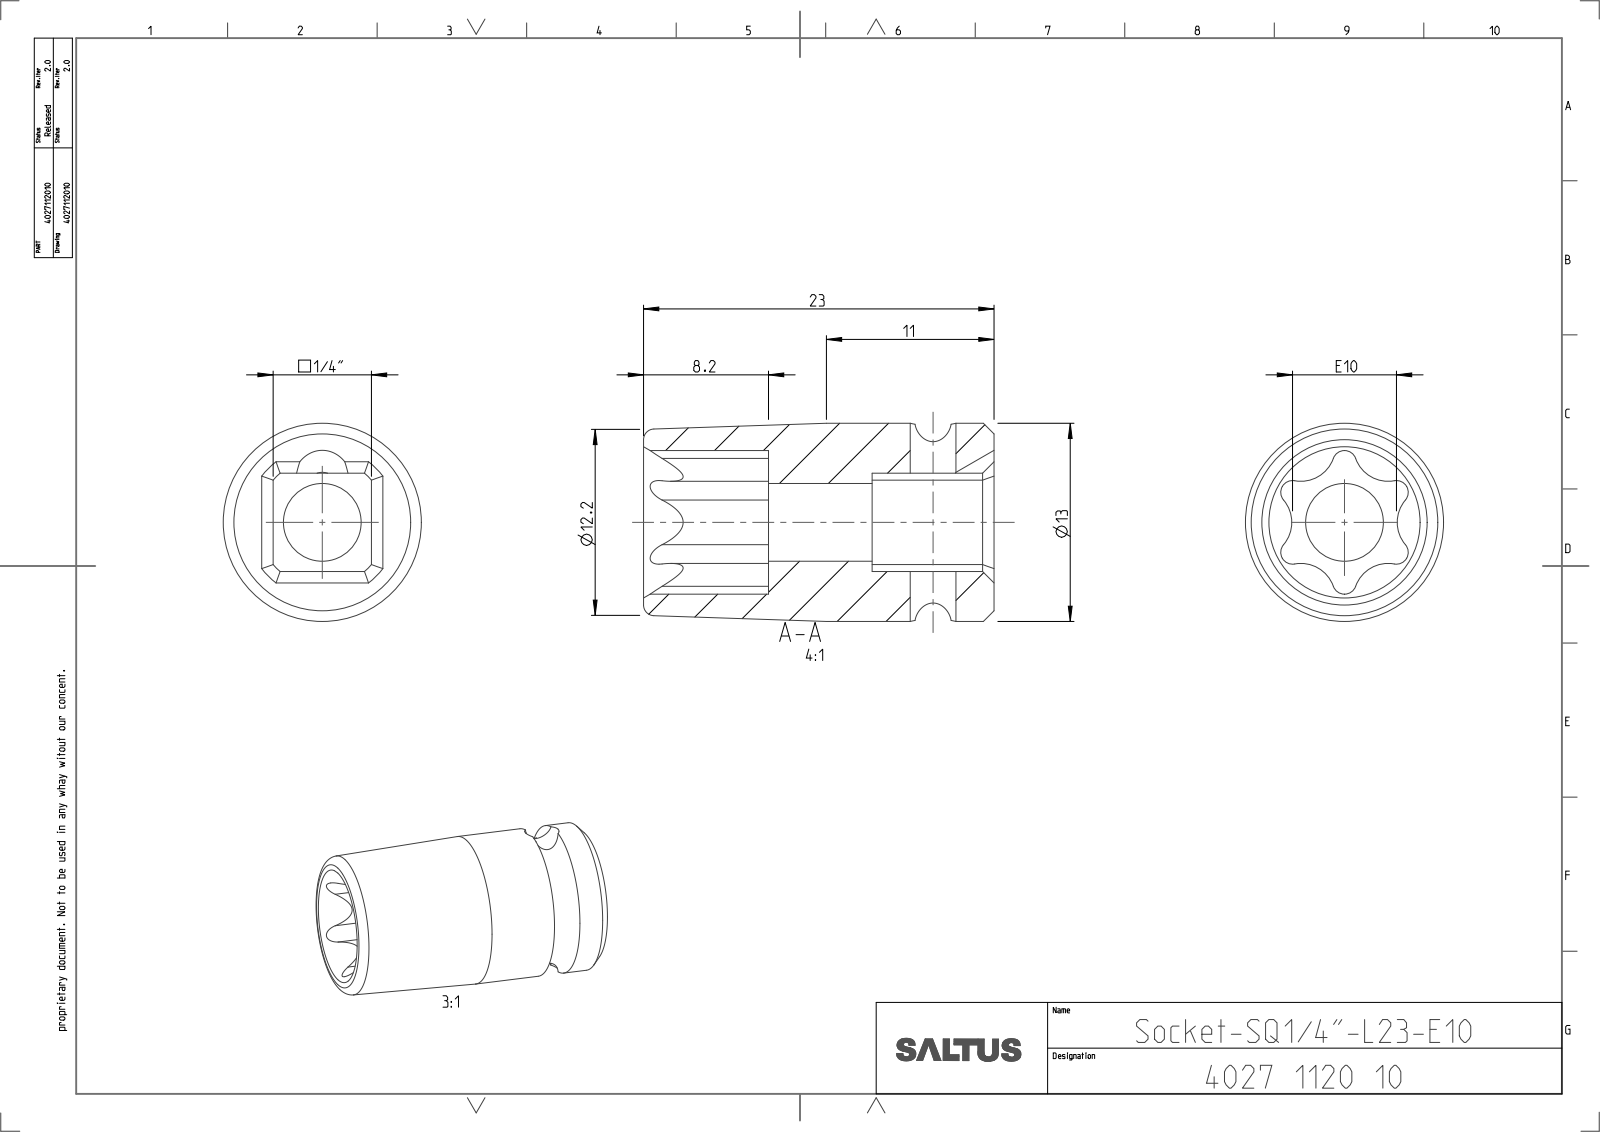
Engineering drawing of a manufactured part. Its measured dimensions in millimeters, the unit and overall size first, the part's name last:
Units: millimetres
Overall size (bounding box): 23 × 13 × 13
Round holes (diameter × count): ⌀3 ×1, ⌀5.1 ×1
Round bosses / shafts (diameter × count): ⌀13 ×1
Partial cylindrical surfaces — rounded edges, fillets, slot ends (radius × count): R0.78 ×6, R2.26 ×6, R2 ×1, R4.25 ×1
Main face-to-face distances: 6.46, 14.8, 8, 6.8, 23, 15, 8.2
Volume: 1 921 mm³ · Surface area: 1 677 mm²
Bodies: 1 solid, 54 faces (13 planar, 27 cylindrical, 14 other)
Part name (STEP PRODUCT): 4027112010
STEP written by: CREO PARAMETRIC BY PTC INC, 2022414 (CONFIG_CONTROL_DESIGN)
